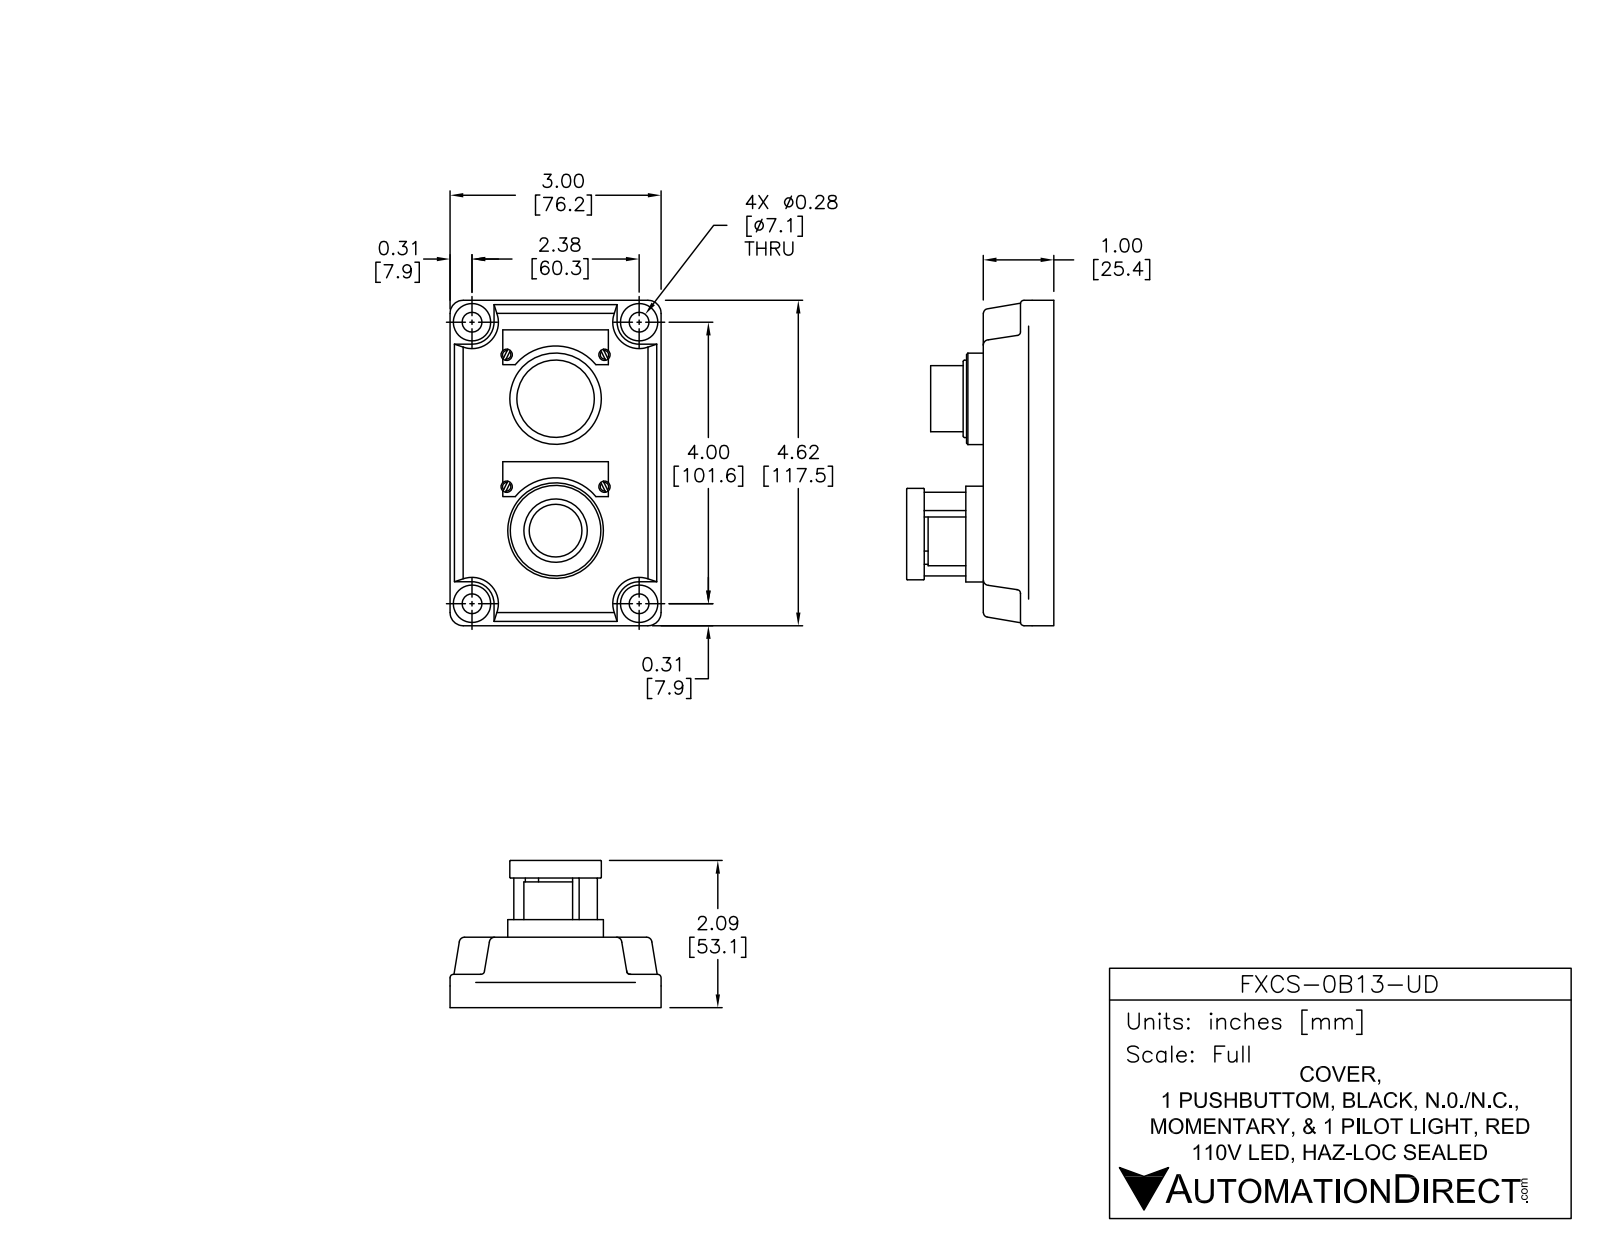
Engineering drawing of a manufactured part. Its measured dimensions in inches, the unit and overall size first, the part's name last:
Units: inches
Overall size (bounding box): 5.31 × 4.989 × 3.69
Round holes (diameter × count): ⌀0.16 ×8, ⌀0.198 ×1, ⌀0.94 ×1, ⌀1.1 ×1
Round bosses / shafts (diameter × count): ⌀0.16 ×8, ⌀0.39 ×4, ⌀1.37 ×1, ⌀1.36 ×1, ⌀1.31 ×1, ⌀1.3 ×1, ⌀1 ×1, ⌀0.9 ×1
Partial cylindrical surfaces — rounded edges, fillets, slot ends (radius × count): R0.02 ×22, R0.05 ×12, R0.055 ×4, R0.06 ×4, R0.075 ×4, R0.185 ×4, R0.42 ×4, R0.653 ×3
Main face-to-face distances: 3.39, 0.49, 2.9, 0.02, 3.69, 0.578, 3.111, 1.19, 0.7, 2.2
Hole centre spacings: 0.25, 2.197, 0.5, 2.183, 2.239, 0.75, 1.168, 1.279
Volume: 49.84 in³ · Surface area: 107.7 in²
Bodies: 1 solid, 750 faces (310 planar, 163 cylindrical, 277 other)
Part name (STEP PRODUCT): FXCS-0B13-UD
STEP written by: SolidWorks 2015 (AUTOMOTIVE_DESIGN)
